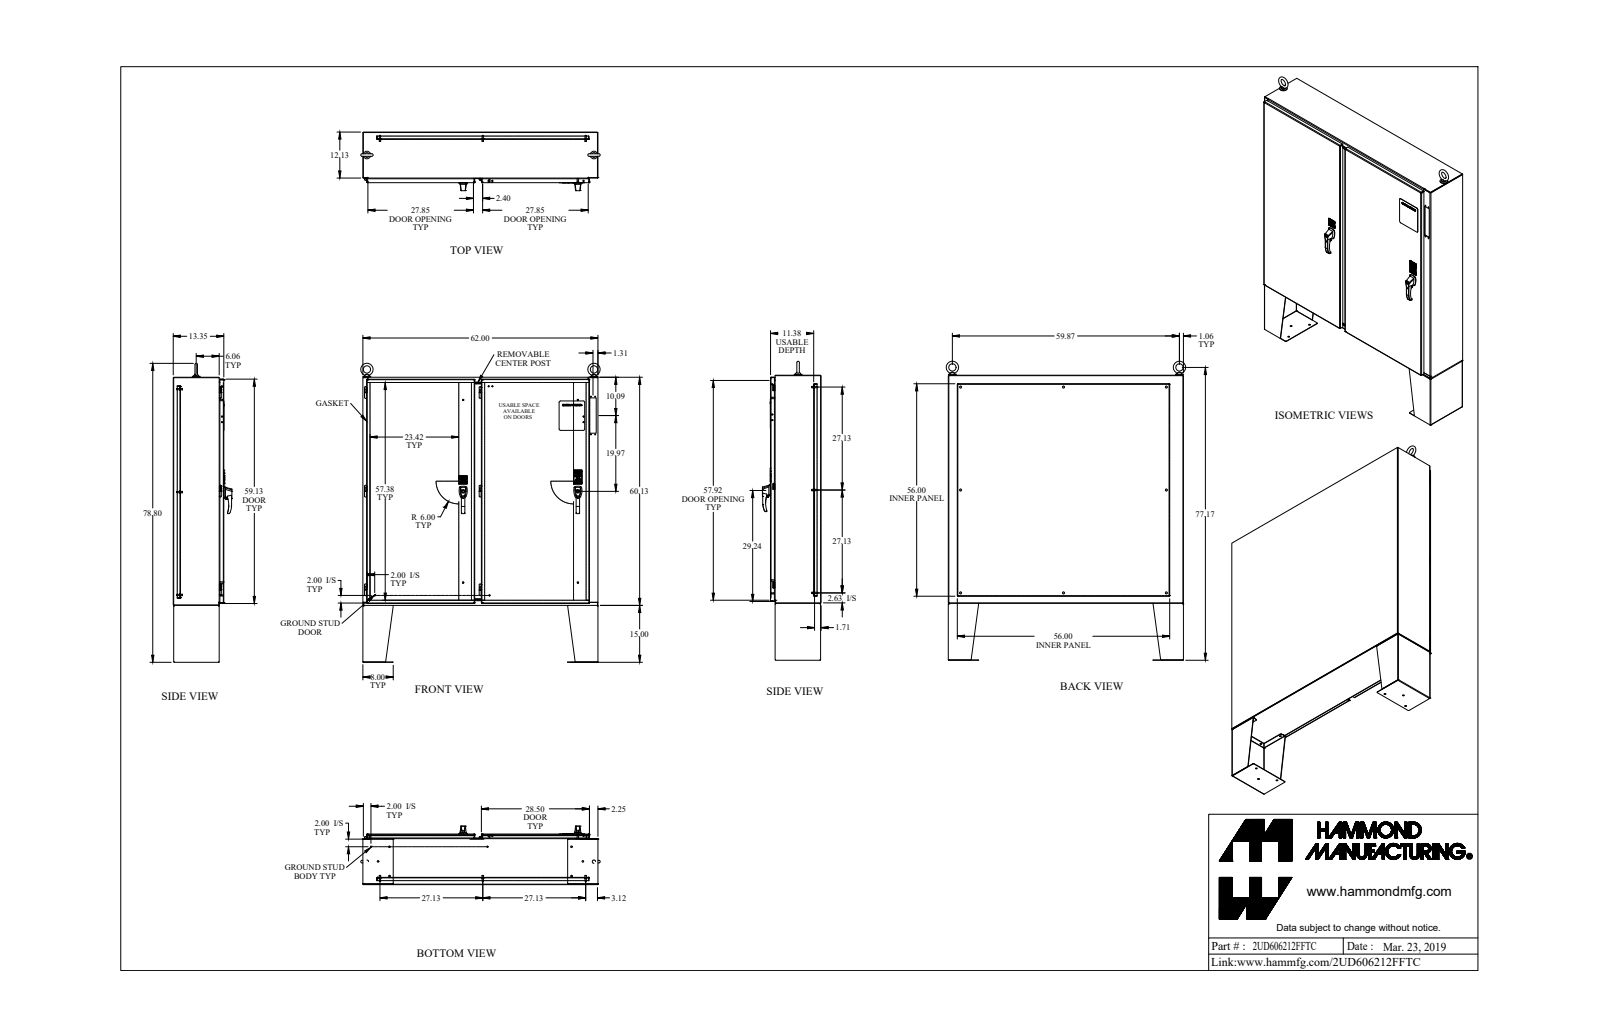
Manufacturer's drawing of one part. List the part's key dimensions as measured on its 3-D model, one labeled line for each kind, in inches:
Part name (STEP PRODUCT): 2UD606212FFTC
STEP written by: SolidWorks 2018 (AUTOMOTIVE_DESIGN)
Units: inches
Bodies: 215 solids, 3339 faces (1892 planar, 959 cylindrical, 488 other)
Overall size (bounding box): 78.799 × 63.122 × 15.466
Volume: 3 390 in³ · Surface area: 35 752 in²
Round holes (diameter × count): ⌀0.437 ×14, ⌀0.281 ×11, ⌀0.307 ×11, ⌀0.196 ×10, ⌀0.25 ×10, ⌀0.35 ×8, ⌀0.257 ×6, ⌀0.313 ×6, ⌀0.445 ×5, ⌀0.28 ×4, ⌀0.282 ×4, ⌀0.375 ×4
Round bosses / shafts (diameter × count): ⌀0.25 ×19, ⌀1 ×14, ⌀0.65 ×9, ⌀0.375 ×9, ⌀0.33 ×9, ⌀0.281 ×8, ⌀0.75 ×6, ⌀0.53 ×6
Partial cylindrical surfaces — rounded edges, fillets, slot ends (radius × count): R0.125 ×62, R0.06 ×51, R0.5 ×38, R0.017 ×32, R0.185 ×30, R0.03 ×28, R0.048 ×20, R0.143 ×20
Main face-to-face distances: 0.125, 0.072, 11.431, 13.368, 13.243, 1.937, 1.812, 1.865, 1.741, 11.503
Hole centre spacings: 1, 4.888, 5.076, 6.126, 9.964, 30.25, 51.147, 54.126
